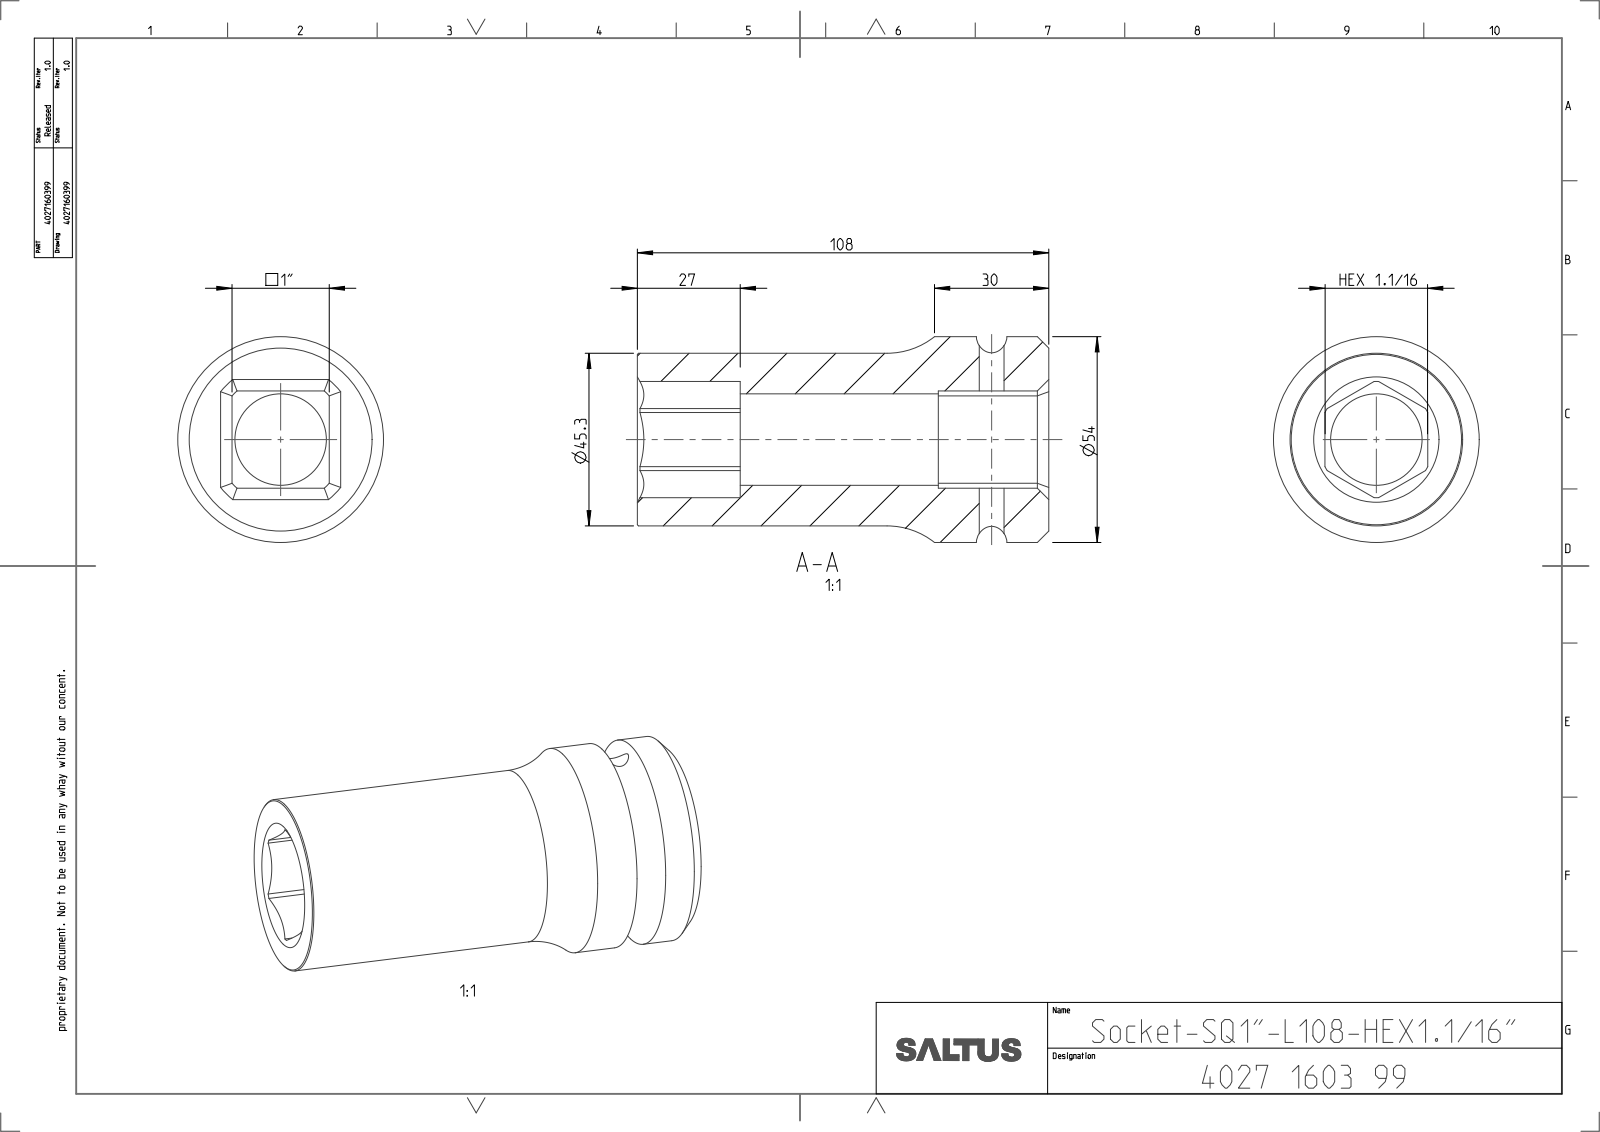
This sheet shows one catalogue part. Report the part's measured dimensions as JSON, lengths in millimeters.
{"part_name": "4027160399", "step_written_by": "CREO PARAMETRIC BY PTC INC, 2022414 (CONFIG_CONTROL_DESIGN)", "units": "millimeters", "bodies": {"solids": 1, "faces": 54, "planar": 18, "cylindrical": 22, "other": 14}, "overall_size": [108, 54, 54], "volume_mm3": 131623, "surface_area_mm2": 29034, "round_holes": [[6.5, 1], [24, 1]], "round_bosses_or_shafts": [[54, 1], [45.3, 1]], "partial_cylinders_radius": [[15.25, 1], [17.15, 1]], "face_to_face_distances": [25.52, 26.98, 0.73, 26.25, 108, 29, 79, 81, 52, 27]}
